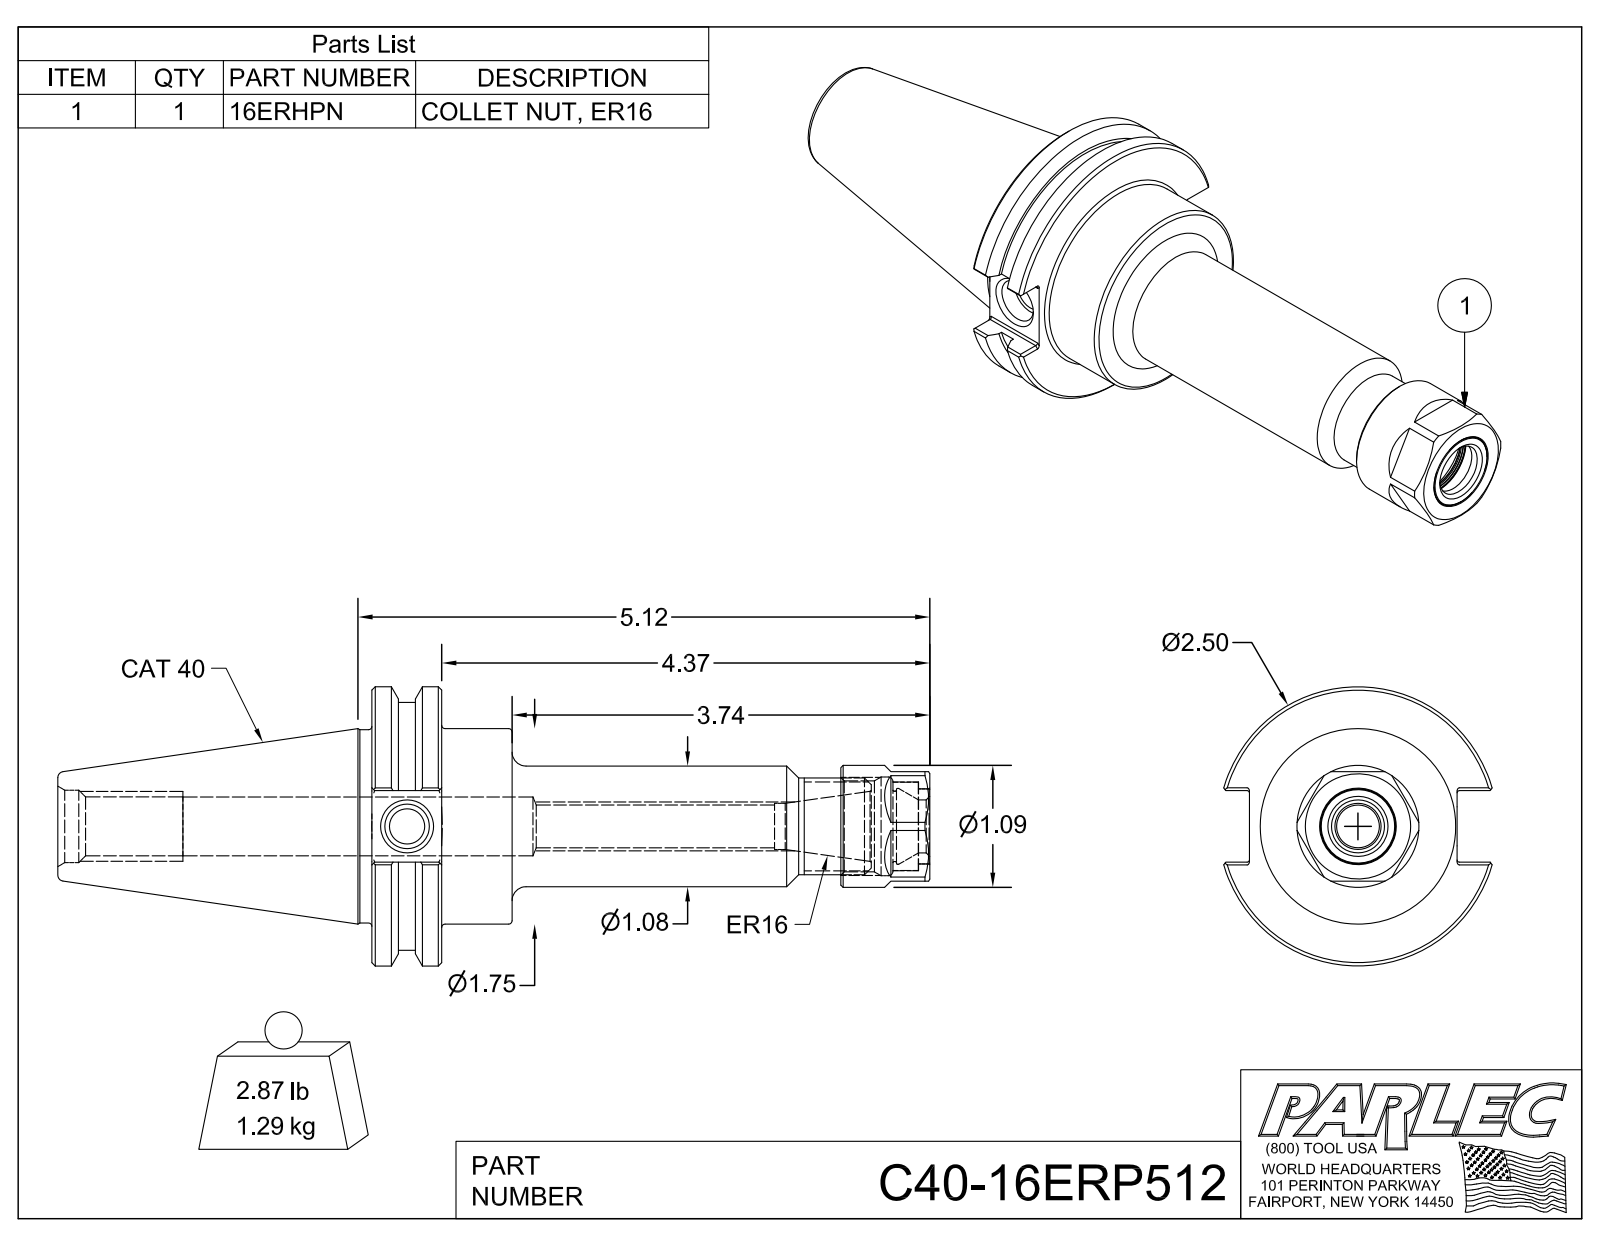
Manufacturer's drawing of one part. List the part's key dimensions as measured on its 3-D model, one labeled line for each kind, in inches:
Part name (STEP PRODUCT): C40-16ERP512; C40-16ER5-1; 16ERHPN
STEP written by: Autodesk Inventor 2018 (AUTOMOTIVE_DESIGN)
Units: inches
Bodies: 3 solids, 130 faces (53 planar, 39 cylindrical, 38 other)
Overall size (bounding box): 7.808 × 2.5 × 2.403
Volume: 10.12 in³ · Surface area: 57.54 in²
Round holes (diameter × count): ⌀0.315 ×1, ⌀0.383 ×1, ⌀0.399 ×1, ⌀0.413 ×1, ⌀0.474 ×1, ⌀0.527 ×1, ⌀0.527 ×1, ⌀0.63 ×1, ⌀0.648 ×1, ⌀0.674 ×1, ⌀0.68 ×1, ⌀0.794 ×1
Round bosses / shafts (diameter × count): ⌀2.5 ×1, ⌀2.219 ×1, ⌀1.75 ×1, ⌀1.73 ×1, ⌀1.092 ×1, ⌀1.08 ×1, ⌀0.866 ×1, ⌀0.79 ×1
Partial cylindrical surfaces — rounded edges, fillets, slot ends (radius × count): R0.02 ×12
Main face-to-face distances: 0.625, 1.255, 0.63, 0.98, 4.995, 4.37, 3.74, 0.17, 0.81, 4.199
